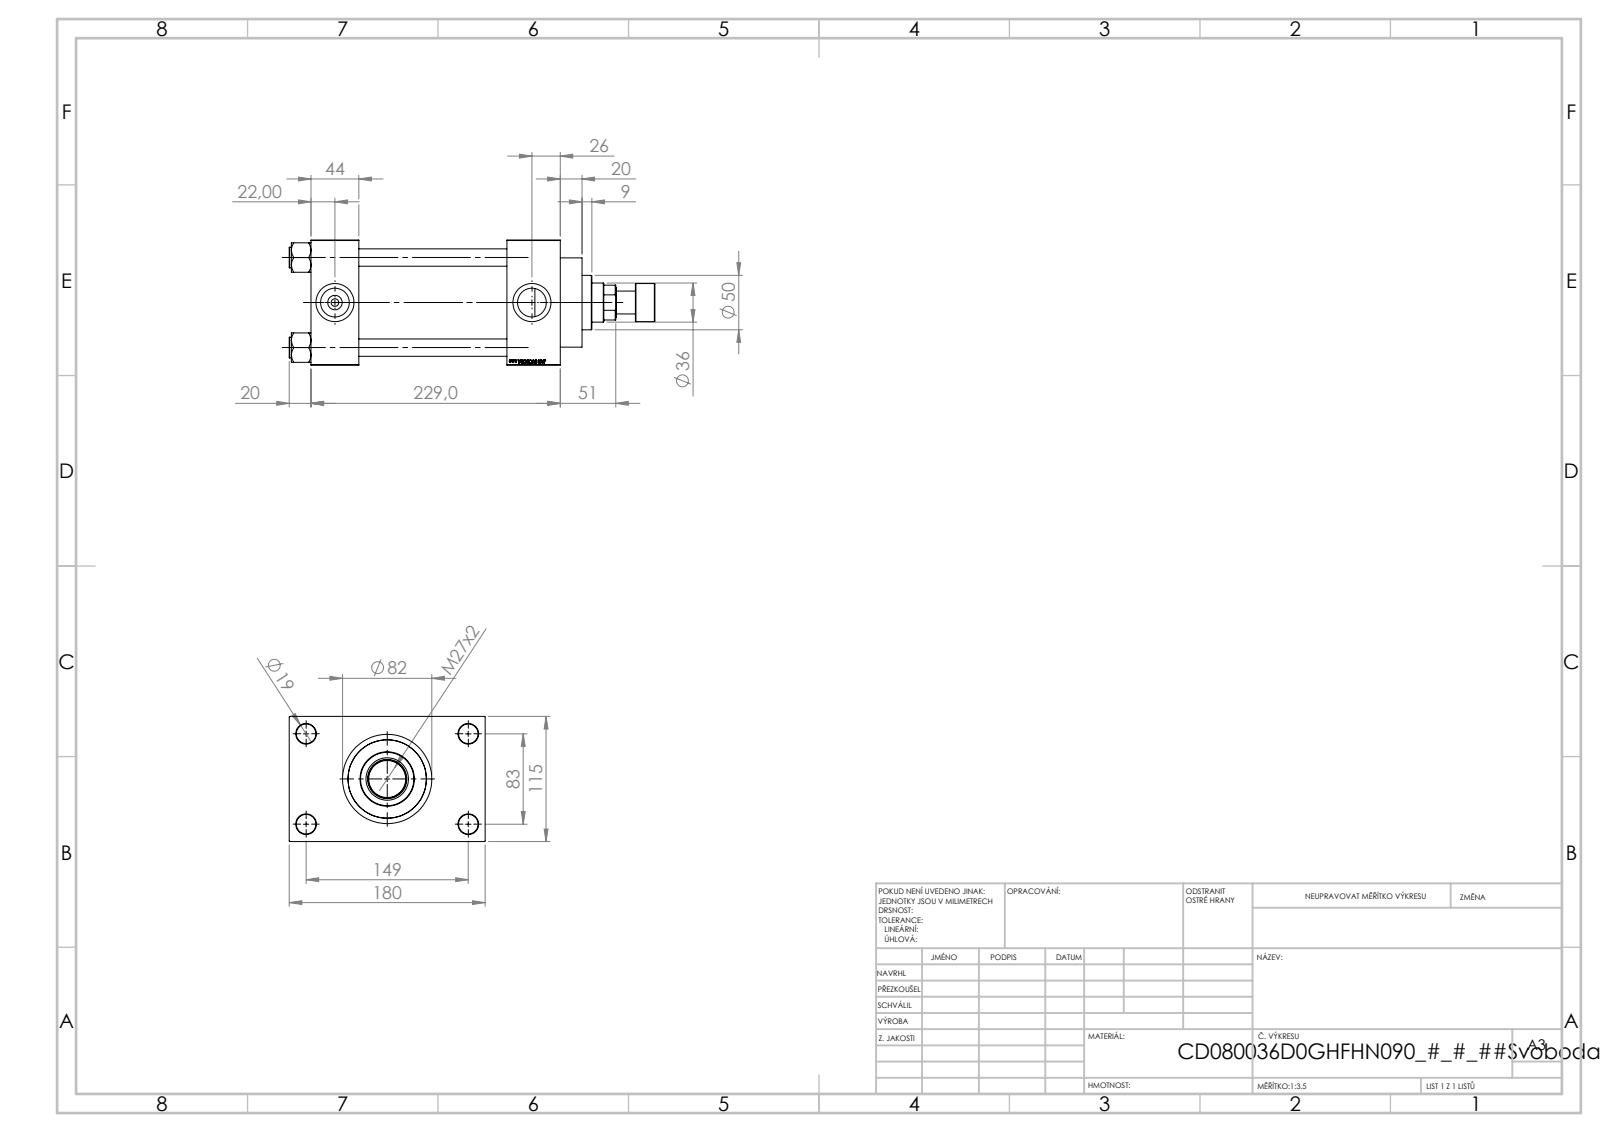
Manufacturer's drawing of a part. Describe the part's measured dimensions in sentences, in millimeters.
The part is named "V215CR_ROD_END_F; V215CD_D_Body; V215CD_VCP_D; V215CD_VC_A (+2 more)". Its 3-D file was written by "SolidWorks 2019 (CONFIG_CONTROL_DESIGN)". It is 12 solids with 1165 faces: 549 planar, 92 cylindrical and 524 other. Overall it measures 336 by 180 by 115 millimeters. Its volume is 2 185 000 cubic millimeters and its surface area 360 658 square millimeters. Round holes: 4 of diameter 16, 4 of diameter 18, 2 of diameter 7, 2 of diameter 26.44, 2 of diameter 35, 1 of diameter 25.5, 1 of diameter 36, 1 of diameter 39, 1 of diameter 61, 1 of diameter 72, 1 of diameter 80. Round bosses or shafts: 4 of diameter 19, 1 of diameter 86, 1 of diameter 82, 1 of diameter 50, 1 of diameter 35, 1 of diameter 21. The main face-to-face distances are 180, 115, 136, 49, 185, 44, 229, 32.5, 147.5, 90. The hole center spacings are 33.15, 58.48, 82.7, 85.28, 89.24, 115.85, 142.43, 83.
